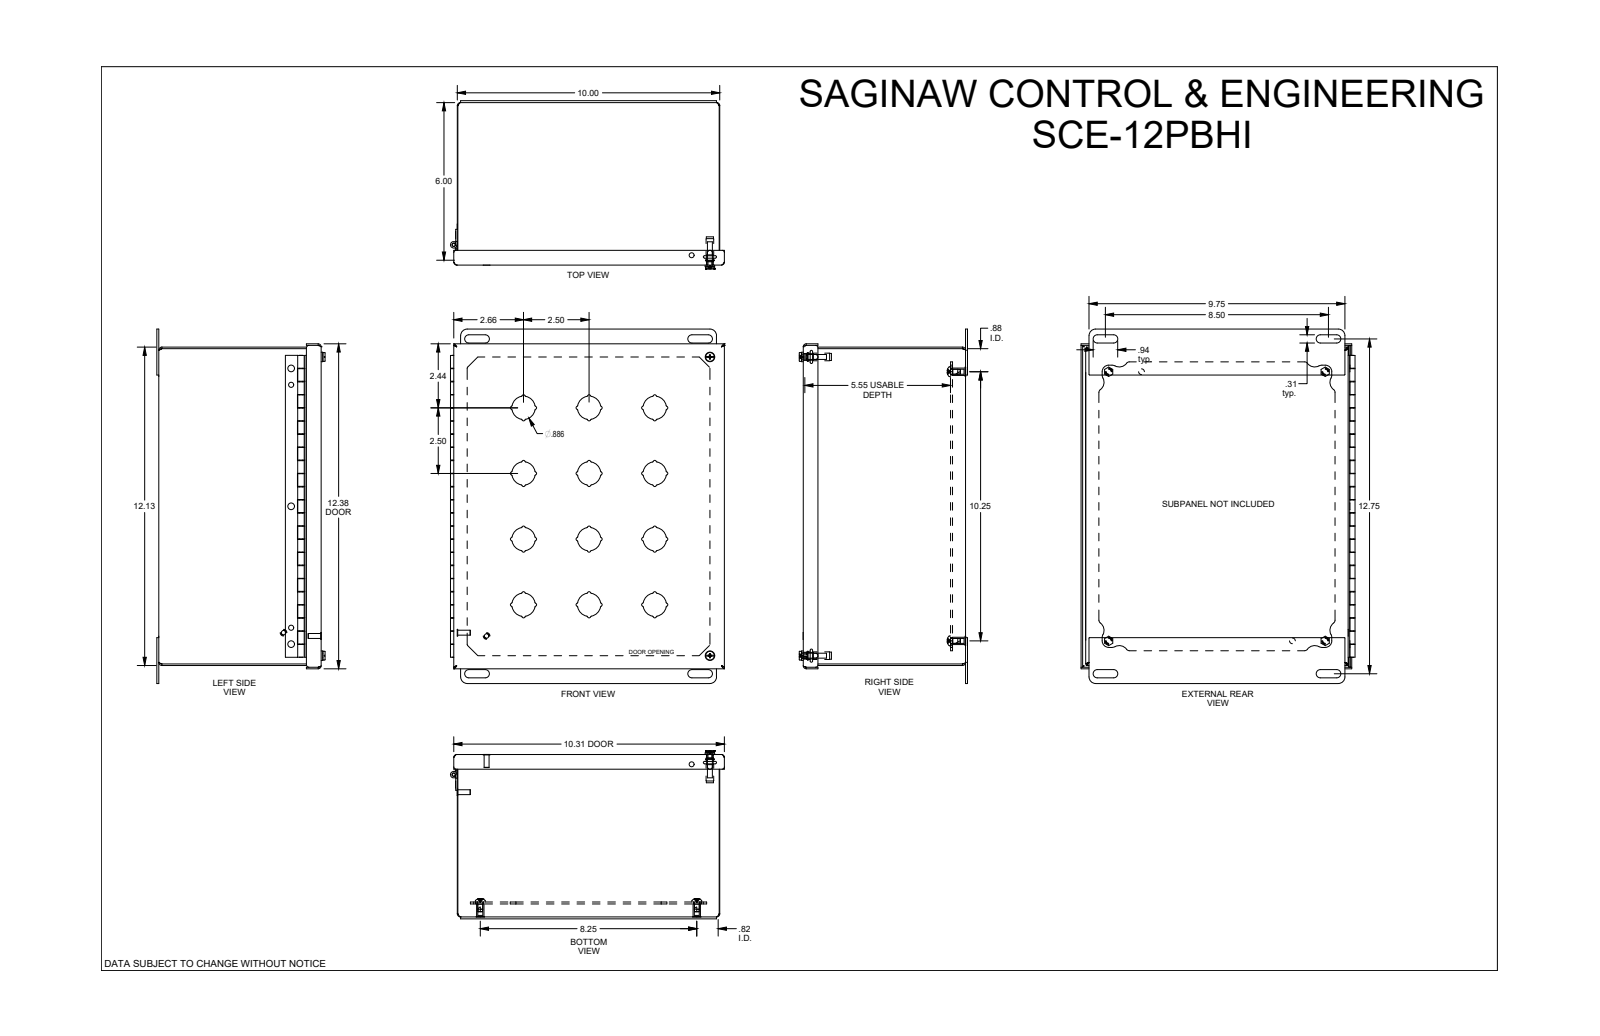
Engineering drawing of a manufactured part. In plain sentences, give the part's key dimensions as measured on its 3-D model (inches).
The part is named "SCE-12PBHI". Its 3-D file was written by "SolidWorks 2019 (AUTOMOTIVE_DESIGN)". It is 22 solids with 890 faces: 369 planar, 453 cylindrical and 68 other. Overall it measures 13.5 by 10.438 by 6.322 inches. Its volume is 46.33 cubic inches and its surface area 1 450 square inches. Round holes: 6 of diameter 0.19, 6 of diameter 0.25, 4 of diameter 0.281, 4 of diameter 0.317, 2 of diameter 0.126, 2 of diameter 0.218, 2 of diameter 0.22, 2 of diameter 0.266, 1 of diameter 0.193. Round bosses or shafts: 5 of diameter 0.256, 5 of diameter 0.188, 4 of diameter 0.437, 4 of diameter 0.28, 2 of diameter 0.362, 2 of diameter 0.34, 2 of diameter 0.292, 2 of diameter 0.27. Partial cylindrical surfaces (rounded edges, fillets, slot ends): 96 of radius 0.04, 48 of radius 0.062, 20 of radius 0.06, 16 of radius 0.25, 13 of radius 0.443, 8 of radius 0.063, 8 of radius 0.125, 8 of radius 0.156. The main face-to-face distances are 0.06, 6.125, 9.94, 6.185, 6.065, 12.065, 0.075, 0.435, 0.51, 5.63. The hole center spacings are 8.768, 0.753, 13.909, 10.824, 13.158, 7, 8.25, 8.25.
